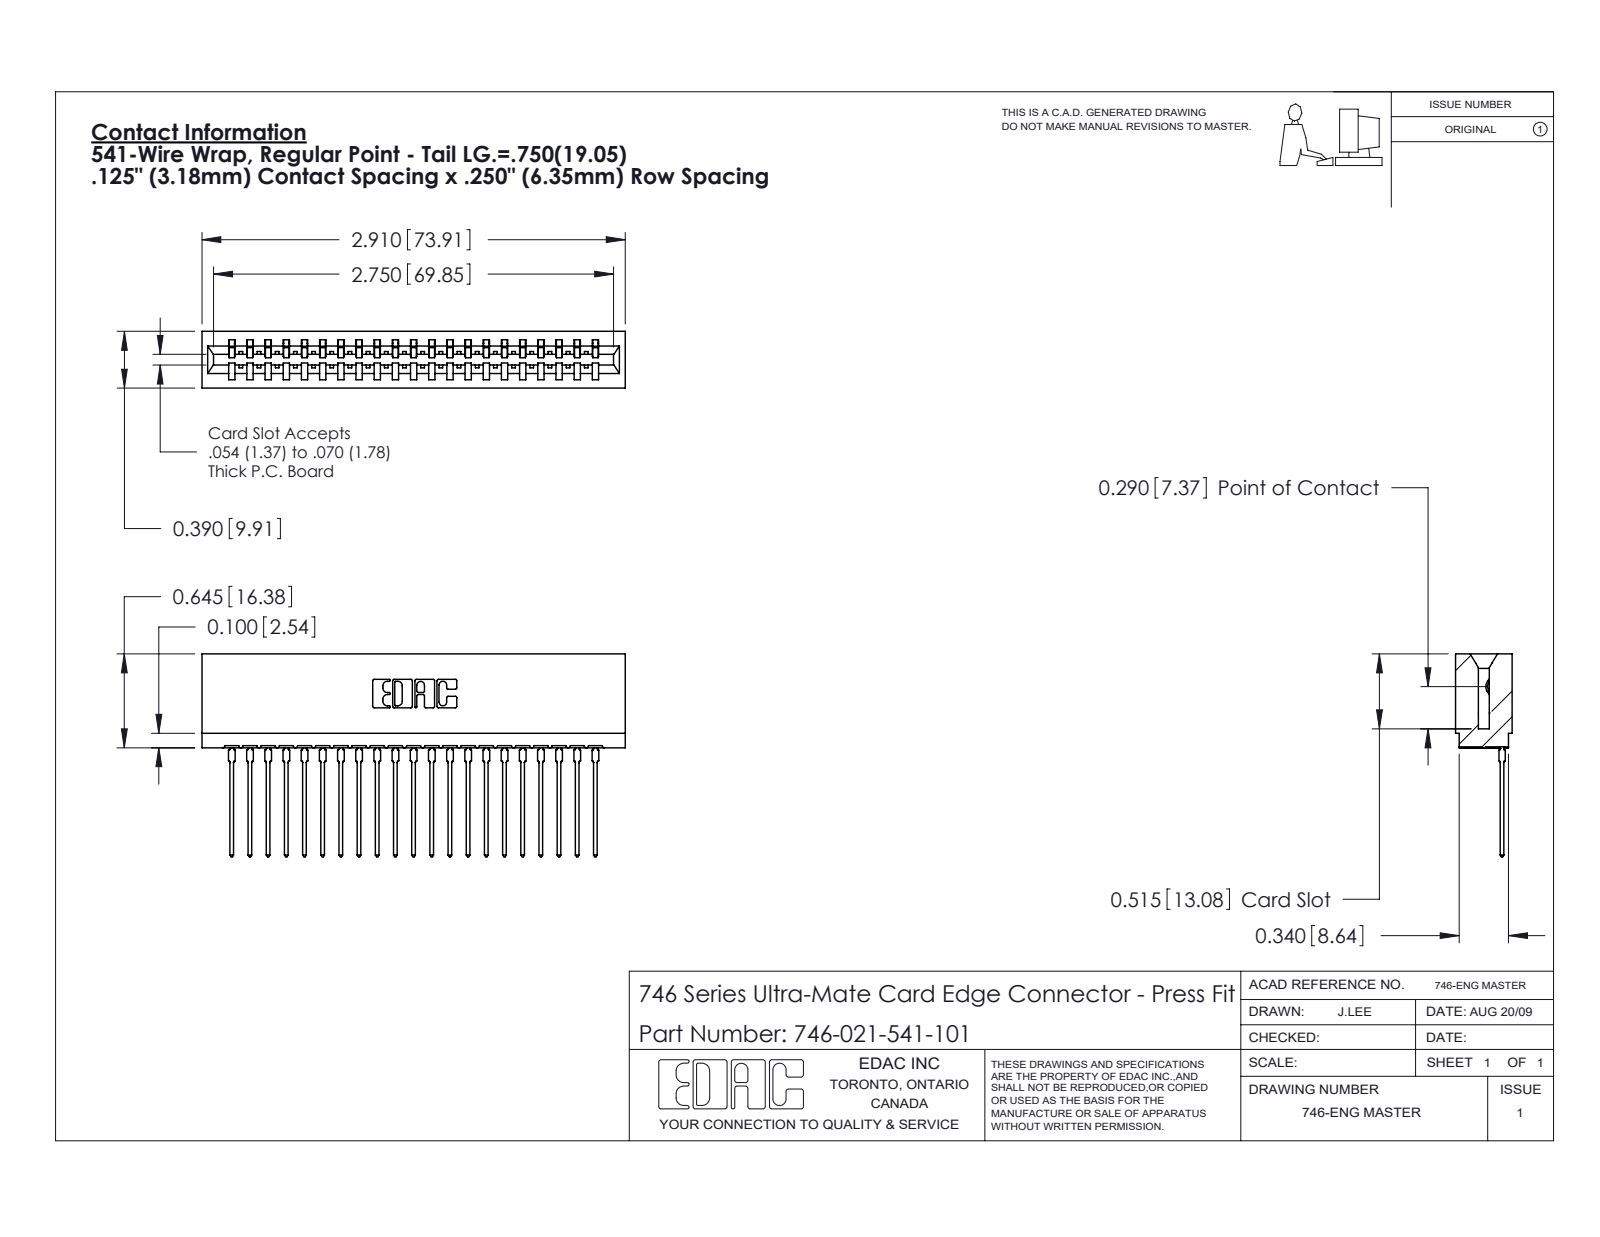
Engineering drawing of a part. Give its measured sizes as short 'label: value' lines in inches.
name: 746-021-541-101; 746 Part_.515 Slot Depth - 01; 746-292-001_541
written by: SolidWorks 2020 (CONFIG_CONTROL_DESIGN)
unit: in
bodies: 22 solids, 2365 faces (1378 planar, 441 cylindrical, 546 other)
size: 2.91 × 1.394 × 0.39
volume: 0.486 in³; area: 18.54 in²
rounds: 42× R0.021, 22× R0.01, 22× R0.015, 6× R0.007, 6× R0.031, 4× R0.005, 4× R0.011, 3× R0.026
face distances: 0.25, 0.333, 0.057, 0.39, 0.5, 0.025, 0.307, 0.083, 0.042, 0.125
